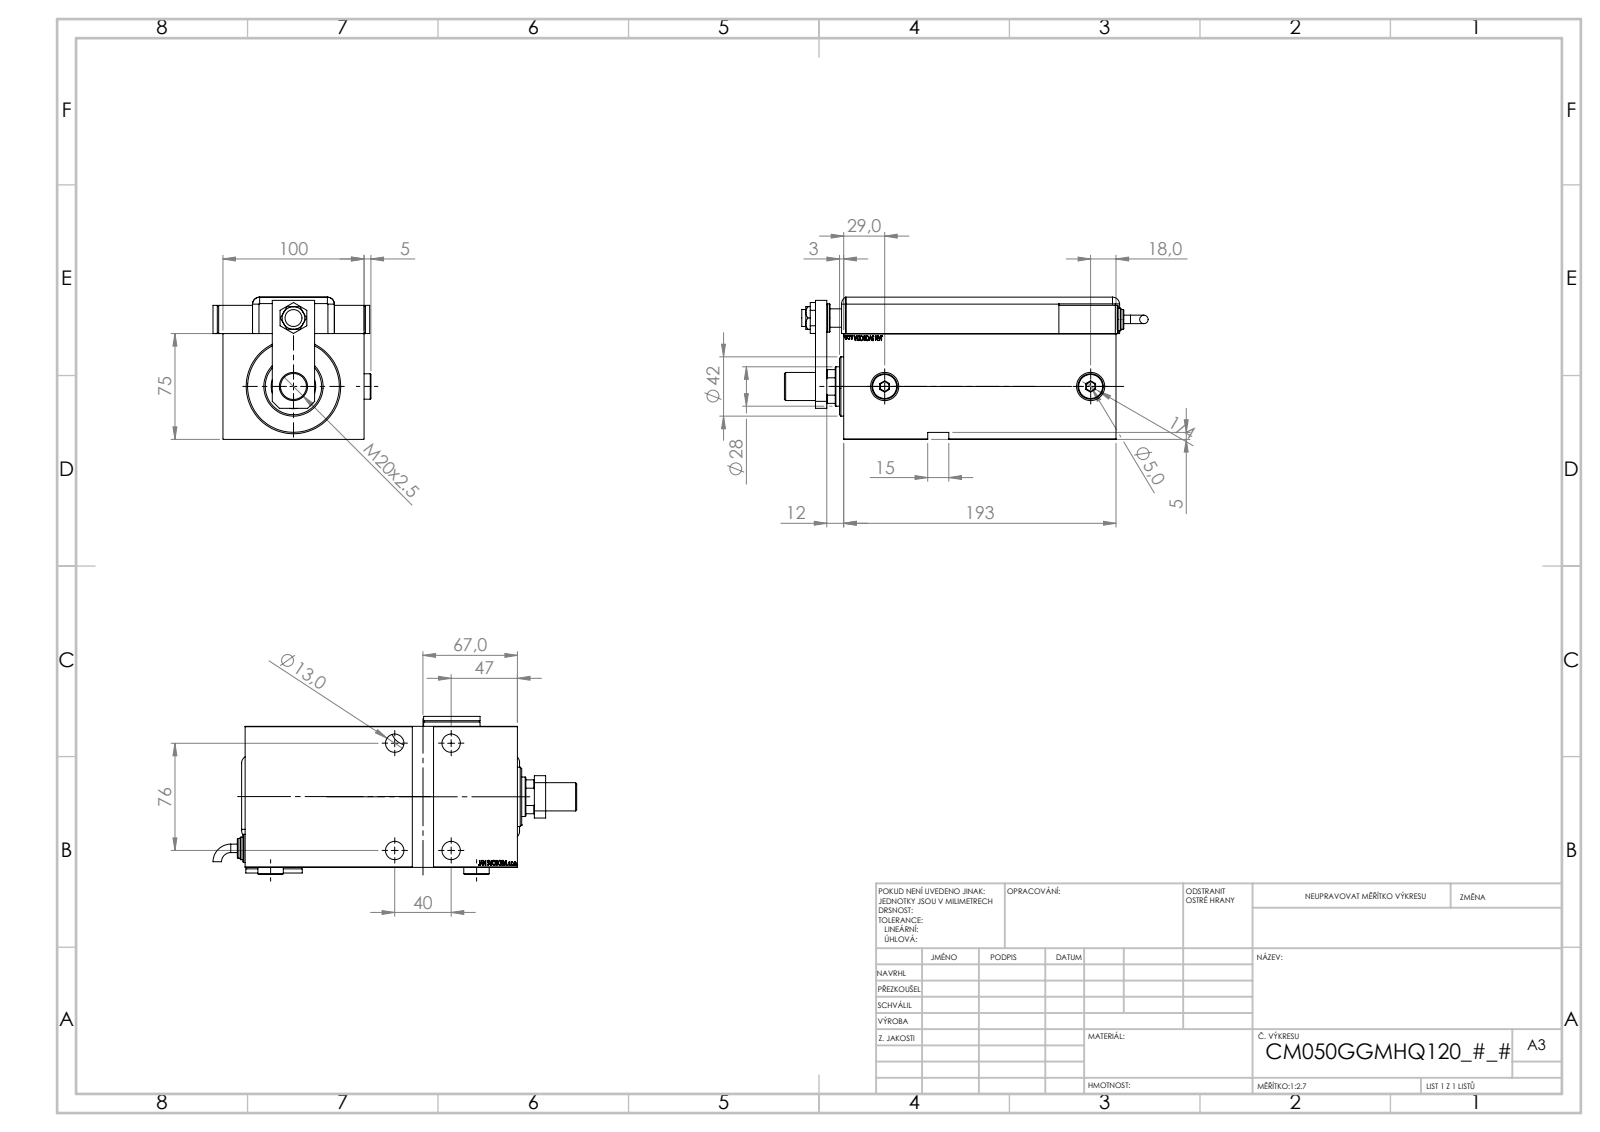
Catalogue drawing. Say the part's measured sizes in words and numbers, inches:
The part is named "V450CM_VC_G; SWITCH_Q_FRONT_BACK; NUT_D19; KRYT (+8 more)". Its 3-D file was written by "SolidWorks 2019 (CONFIG_CONTROL_DESIGN)". It is 16 solids with 1294 faces: 652 planar, 115 cylindrical and 527 other. Overall it measures 10.148 by 4.406 by 3.969 inches. Its volume is 86.04 cubic inches and its surface area 373.6 square inches. Round holes: 5 of diameter 0.512, 4 of diameter 0.748, 3 of diameter 0.787, 2 of diameter 0.157, 2 of diameter 0.197, 2 of diameter 0.315, 2 of diameter 0.518, 1 of diameter 0.472, 1 of diameter 0.551, 1 of diameter 0.728, 1 of diameter 1.102, 1 of diameter 1.24. Round bosses or shafts: 3 of diameter 0.787, 3 of diameter 0.709, 2 of diameter 0.63, 2 of diameter 0.551, 2 of diameter 0.236, 1 of diameter 1.654. Partial cylindrical surfaces (rounded edges, fillets, slot ends): 9 of radius 0.197, 1 of radius 0.394, 1 of radius 0.531. The main face-to-face distances are 2.953, 0.118, 3.937, 3.969, 1.016, 0.898, 3.85, 0.827, 3.11, 2.992. The hole center spacings are 1.575, 1.858, 2.41, 2.992, 3.263, 3.381, 3.606, 0.787.
